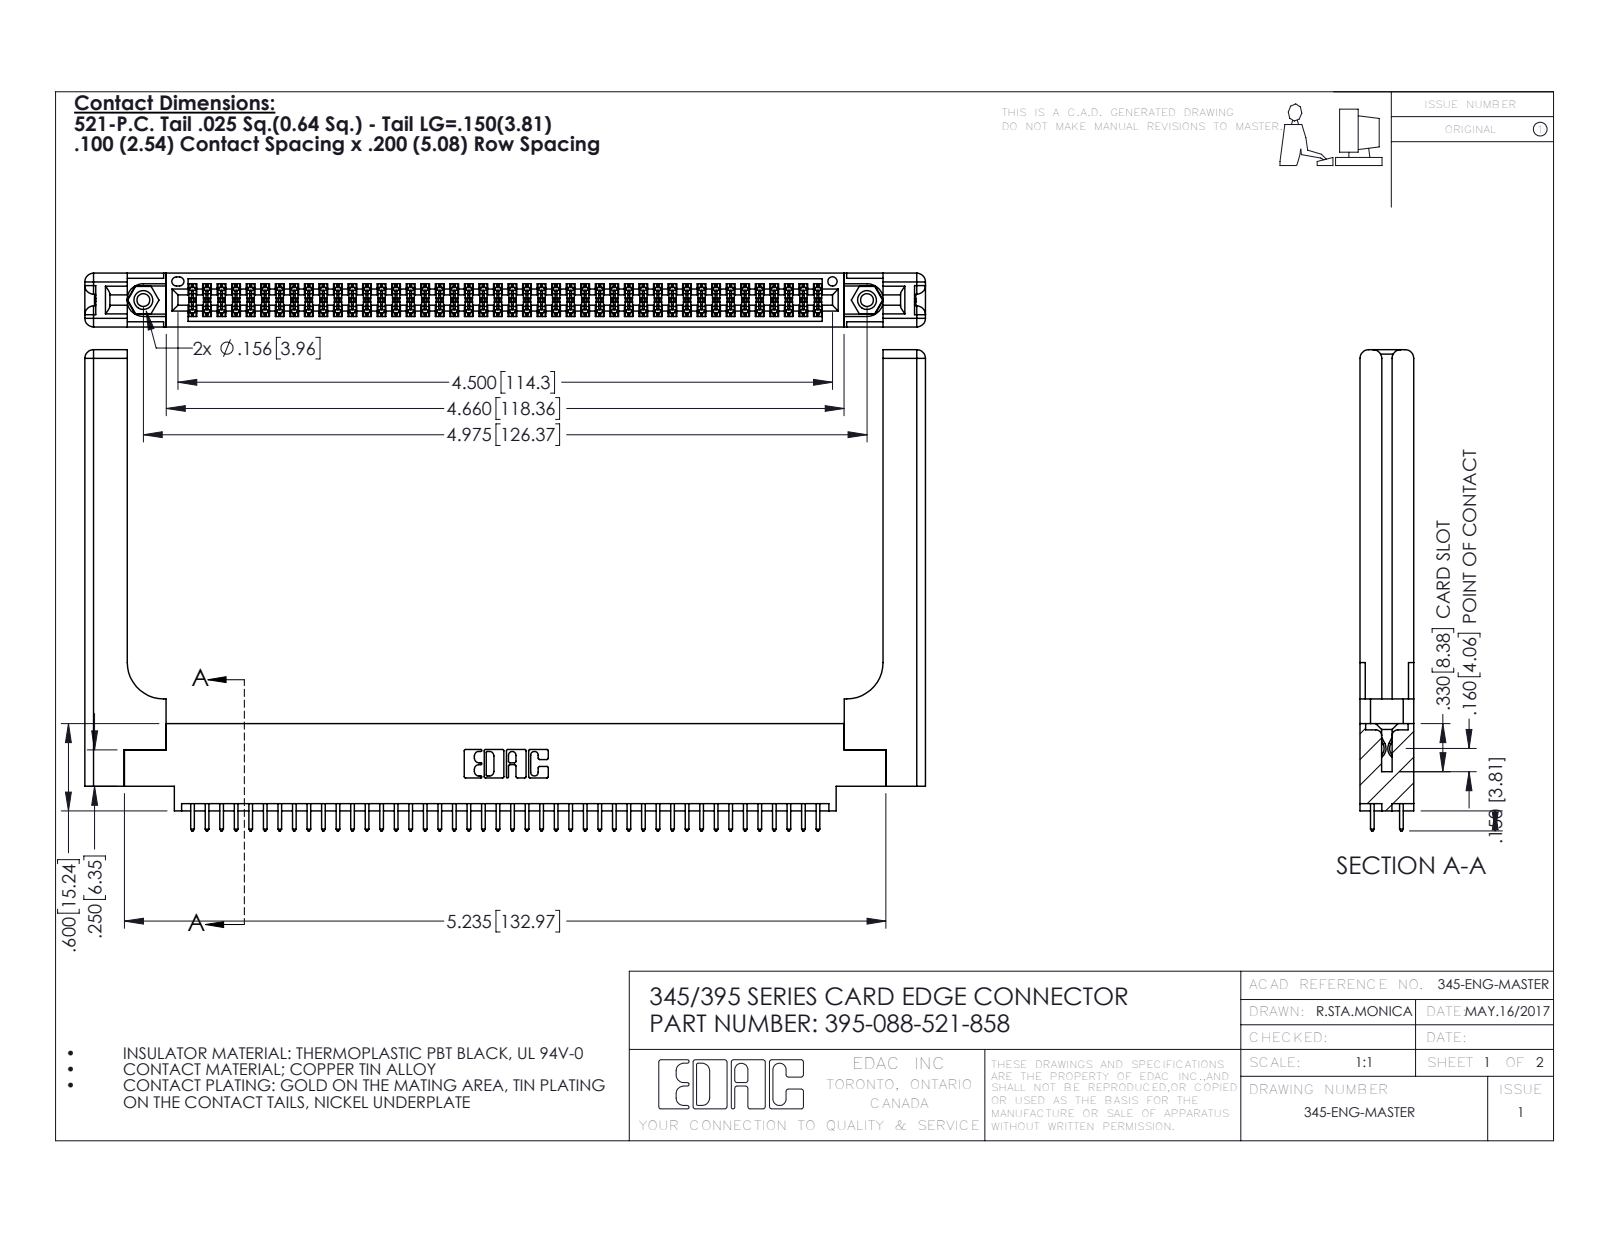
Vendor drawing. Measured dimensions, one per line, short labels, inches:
name: 345-292-001_345-293-121; 345-220-058_345-220-058; 345 Part_0.170 Offset - 0.156 Dia-TH; 345-250-001_345-250-001-102 (+1 more)
written by: SolidWorks 2016 (CONFIG_CONTROL_DESIGN)
unit: in
bodies: 93 solids, 4786 faces (3136 planar, 1590 cylindrical, 60 other)
size: 5.779 × 3.307 × 0.37
volume: 1.379 in³; area: 40.13 in²
holes: 2× ⌀0.089, 2× ⌀0.125, 2× ⌀0.156, 1× ⌀0.064
bosses: 2× ⌀0.155
rounds: 132× R0.006, 88× R0.01, 22× R0.01, 16× R0.06, 6× R0.007, 6× R0.031, 3× R0.026, 2× R0.014
face distances: 0.072, 0.37, 0.298, 0.098, 0.272, 0.025, 0.2, 0.225, 0.175, 0.148
hole spacings: 0.27, 4.739, 4.975
